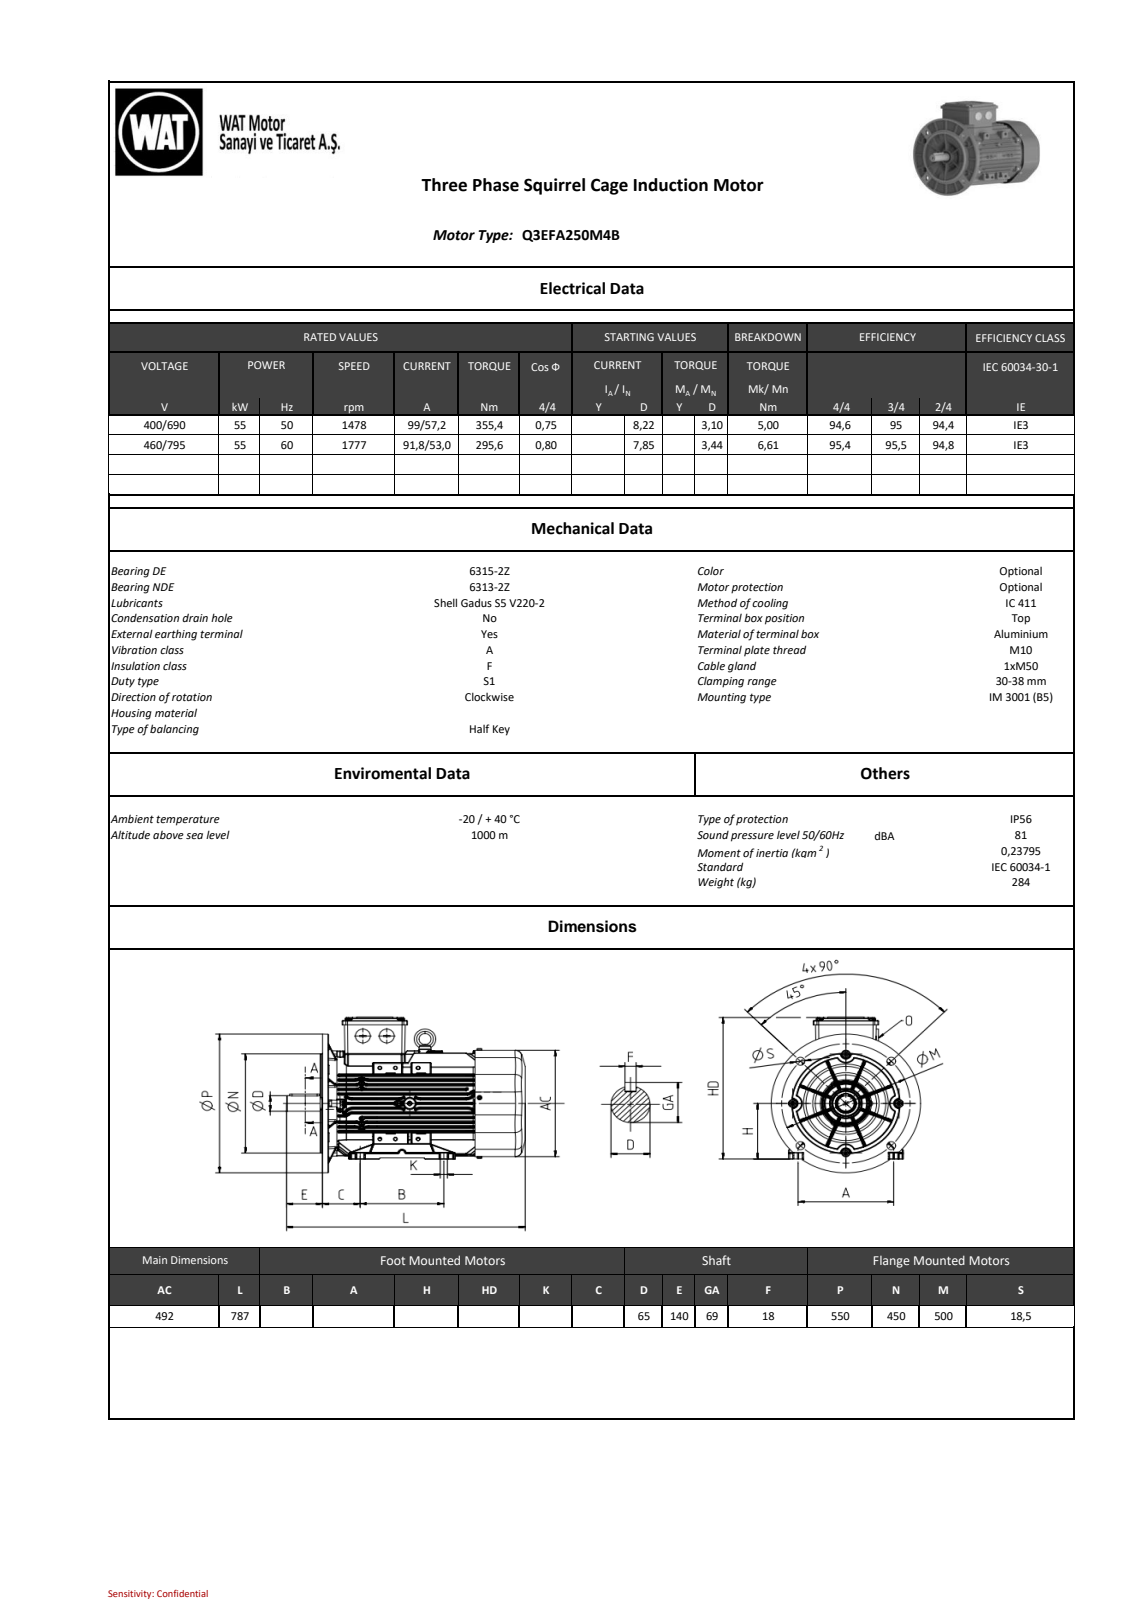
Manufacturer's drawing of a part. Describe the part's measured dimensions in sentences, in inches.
The part is named "001_objects". Its 3-D file was written by "SIEMENS PLM Software NX2206.8101 (AUTOMOTIVE_DESIGN)". It is 0 solids with 14431 faces: 6514 planar, 3813 cylindrical and 4104 other. Overall it measures 30.984 by 21.949 by 21.654 inches. Round holes: 9 of diameter 0.335, 8 of diameter 0.236, 8 of diameter 0.36, 8 of diameter 0.748, 7 of diameter 0.402, 6 of diameter 0.028, 5 of diameter 0.197, 5 of diameter 0.295, 5 of diameter 0.433, 5 of diameter 0.728, 4 of diameter 0.169, 4 of diameter 0.217. Round bosses or shafts: 14 of diameter 0.394, 8 of diameter 0.619, 7 of diameter 0.713, 4 of diameter 0.583, 4 of diameter 0.501, 4 of diameter 0.315, 4 of diameter 0.197, 3 of diameter 0.23. Partial cylindrical surfaces (rounded edges, fillets, slot ends): 966 of radius 0.039, 332 of radius 0.008, 328 of radius 0.079, 271 of radius 0.02, 237 of radius 0.197, 150 of radius 0.098, 87 of radius 0.157, 49 of radius 0.04. The main face-to-face distances are 0.354, 7.473, 0.611, 6.655, 0.818, 0.584, 0.197, 7.267, 0.206, 0.118. The hole center spacings are 6.142, 5.761, 2.684, 9.213, 3.812, 5.354, 6.707, 9.096.
